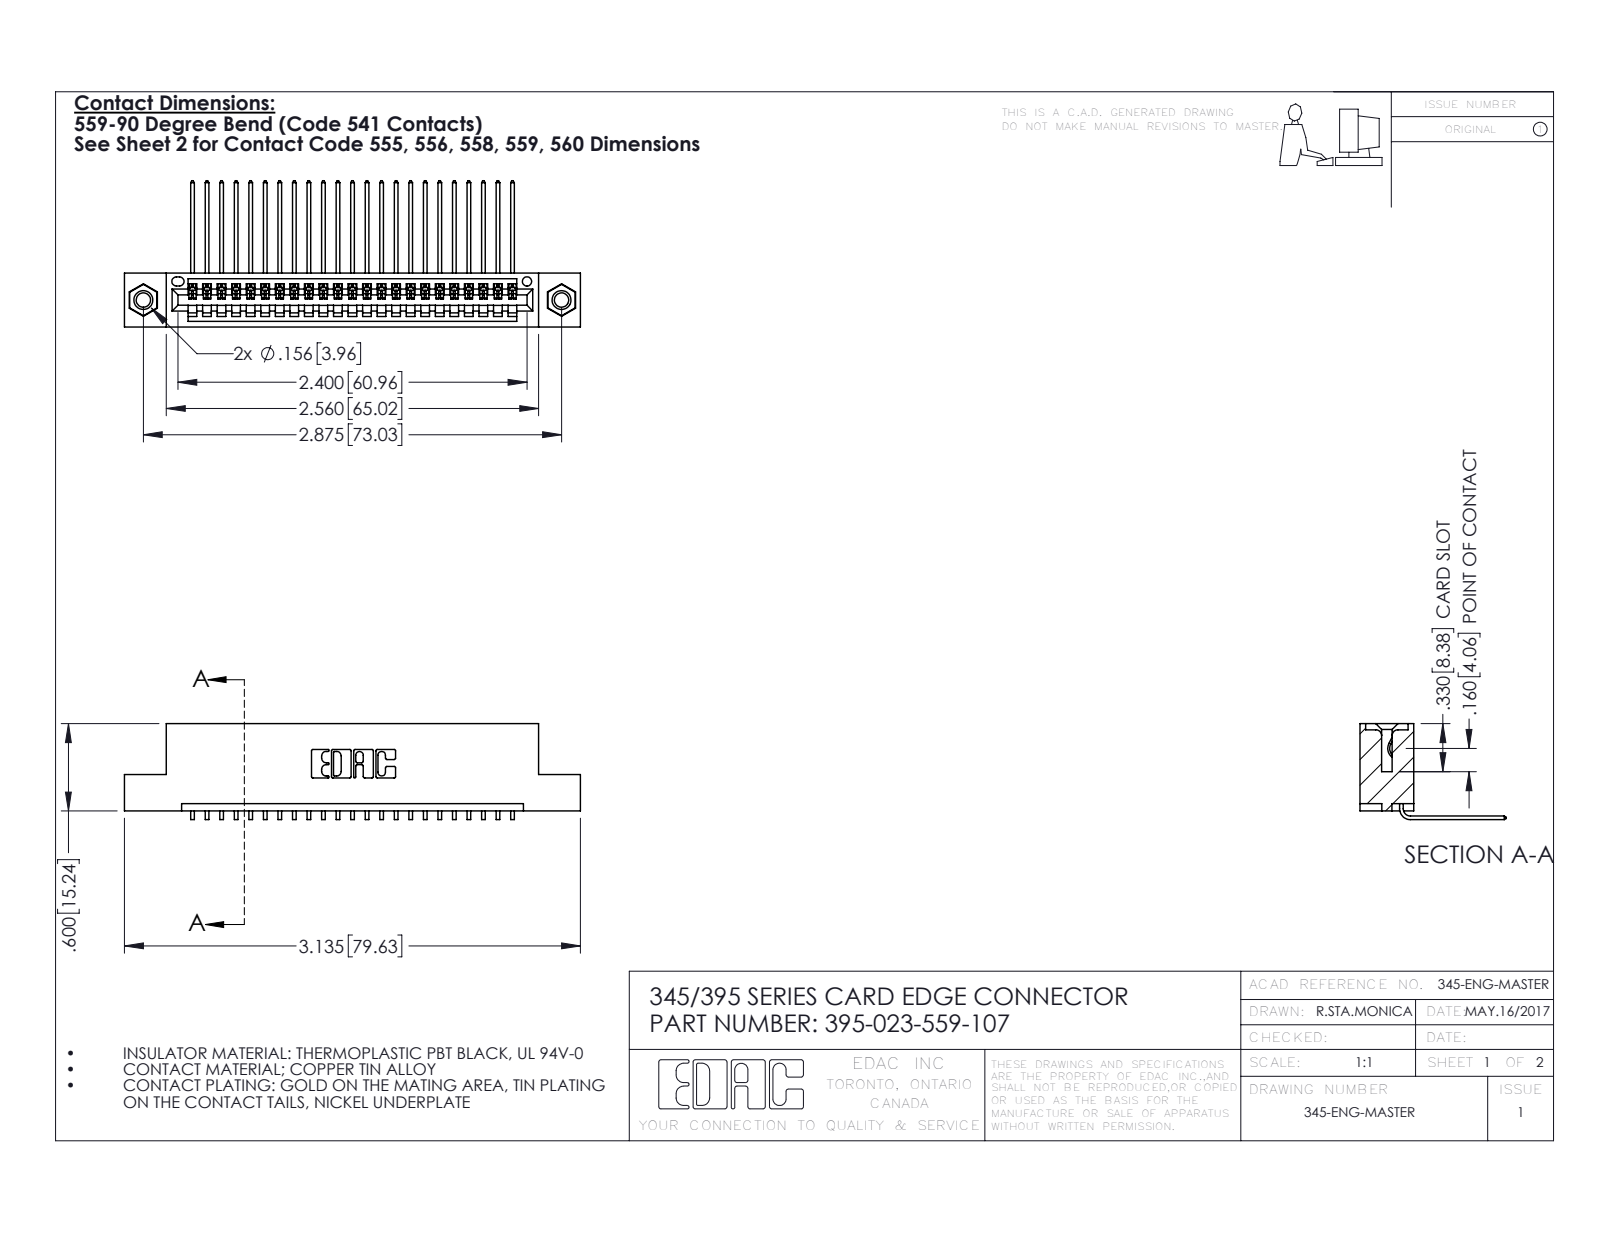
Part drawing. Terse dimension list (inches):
name: 345-250-001_345-250-005-103; 345-292-001_558 559 Tail - 1; 345 Part_Flush Mounting Lugs - 0.156 Dia-TI; 395-023-559-107
written by: SolidWorks 2016 (CONFIG_CONTROL_DESIGN)
unit: in
bodies: 26 solids, 1566 faces (1078 planar, 472 cylindrical, 16 other)
size: 3.135 × 1.005 × 0.659
volume: 0.456 in³; area: 15.74 in²
holes: 2× ⌀0.098, 2× ⌀0.125, 2× ⌀0.156, 1× ⌀0.064
bosses: 2× ⌀0.155
rounds: 46× R0.006, 22× R0.01, 6× R0.007, 6× R0.031, 3× R0.026, 2× R0.031, 2× R0.04, 1× R0.014
face distances: 0.072, 0.298, 0.37, 0.2, 0.098, 0.272, 0.025, 0.225, 0.149, 0.072
hole spacings: 0.27, 2.641, 2.875
